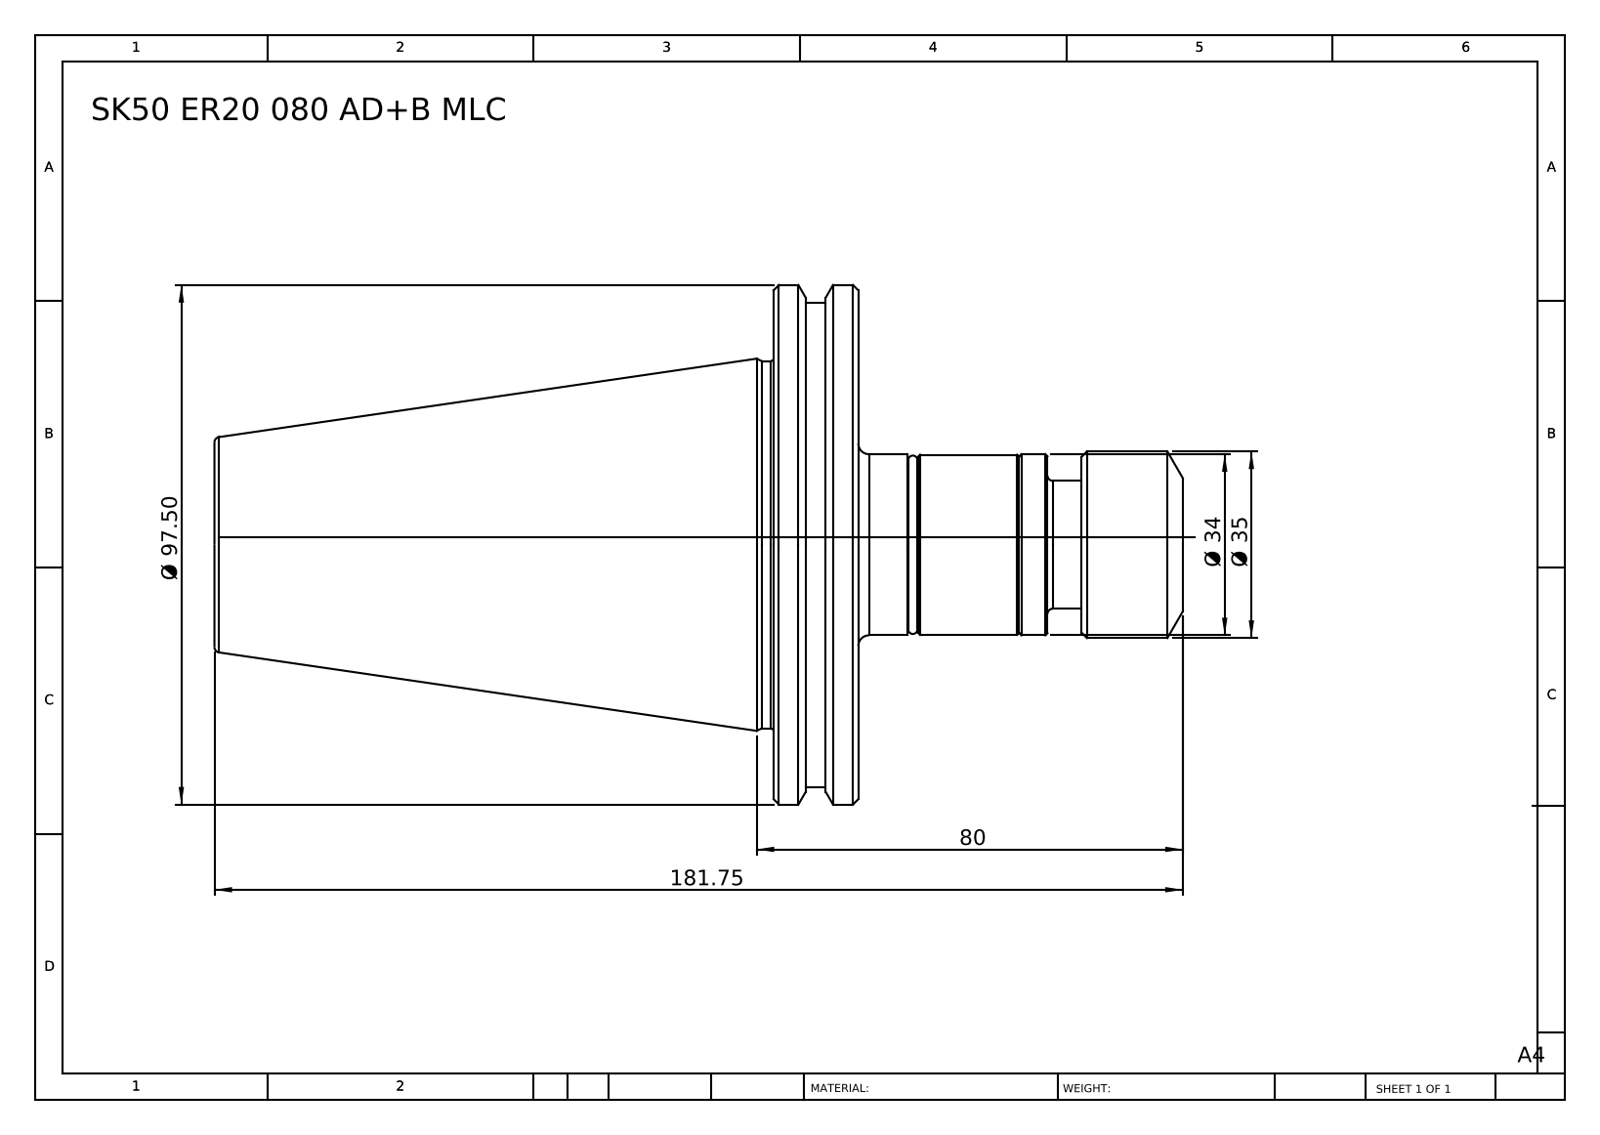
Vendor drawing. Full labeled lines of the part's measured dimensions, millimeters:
Part name (STEP PRODUCT): SK 50 ER 20 080 AD+B MLC
STEP written by: SolidWorks 2014 (CONFIG_CONTROL_DESIGN)
Units: millimetres
Bodies: 2 solids, 67 faces (11 planar, 20 cylindrical, 36 other)
Overall size (bounding box): 181.75 × 97.5 × 97.5
Volume: 425 909 mm³ · Surface area: 44 459 mm²
Round bosses / shafts (diameter × count): ⌀97.5 ×1, ⌀91 ×1, ⌀69 ×1, ⌀35 ×1, ⌀34 ×1, ⌀33.8 ×1, ⌀29.9 ×1, ⌀24 ×1
Main face-to-face distances: 15.9, 120.85, 104.95, 60.9, 76.8, 181.75, 19, 41.9, 57.8, 162.75
